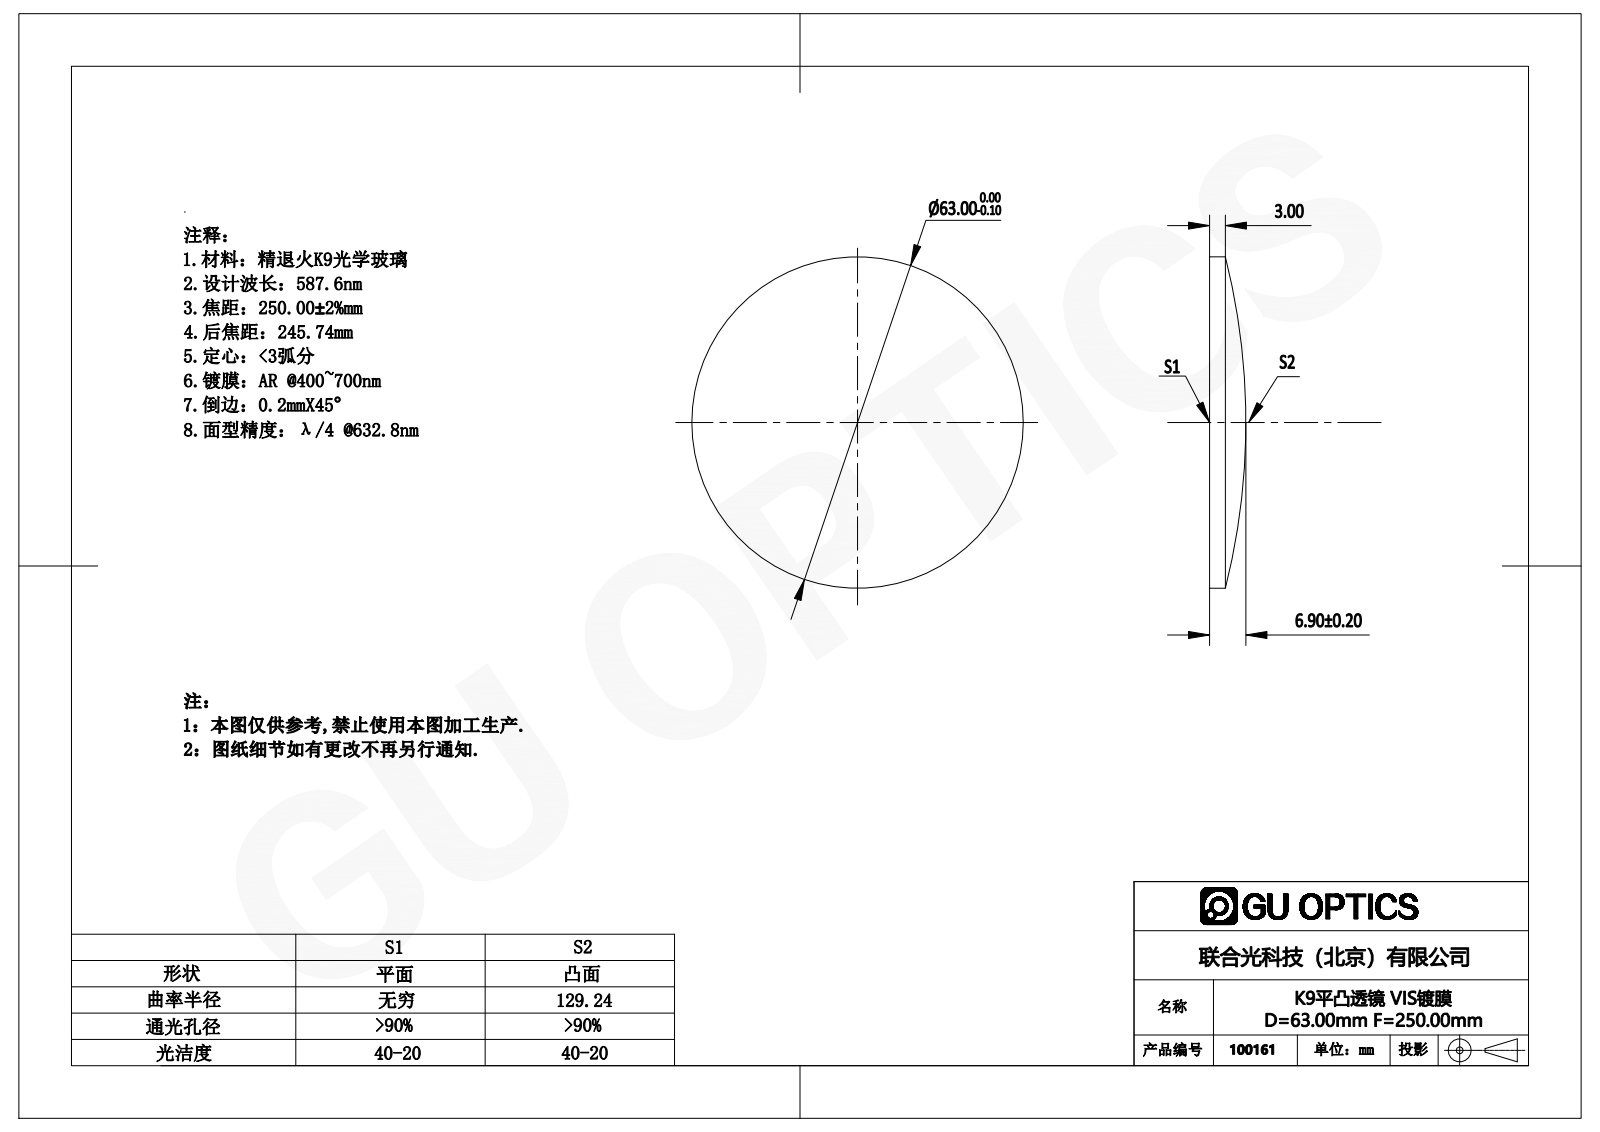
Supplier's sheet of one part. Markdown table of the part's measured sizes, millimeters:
| quantity | value |
| --- | --- |
| part name | 100161 |
| STEP written by | SolidWorks 2016 (AUTOMOTIVE_DESIGN) |
| units | millimeters |
| bodies | 1 solid, 5 faces (1 planar, 2 cylindrical, 2 other) |
| overall size | 63 × 63 × 6.9 |
| volume | 15 461 mm³ |
| surface area | 6 876 mm² |
| round bosses / shafts (diameter × count) | 63 × 1 |
